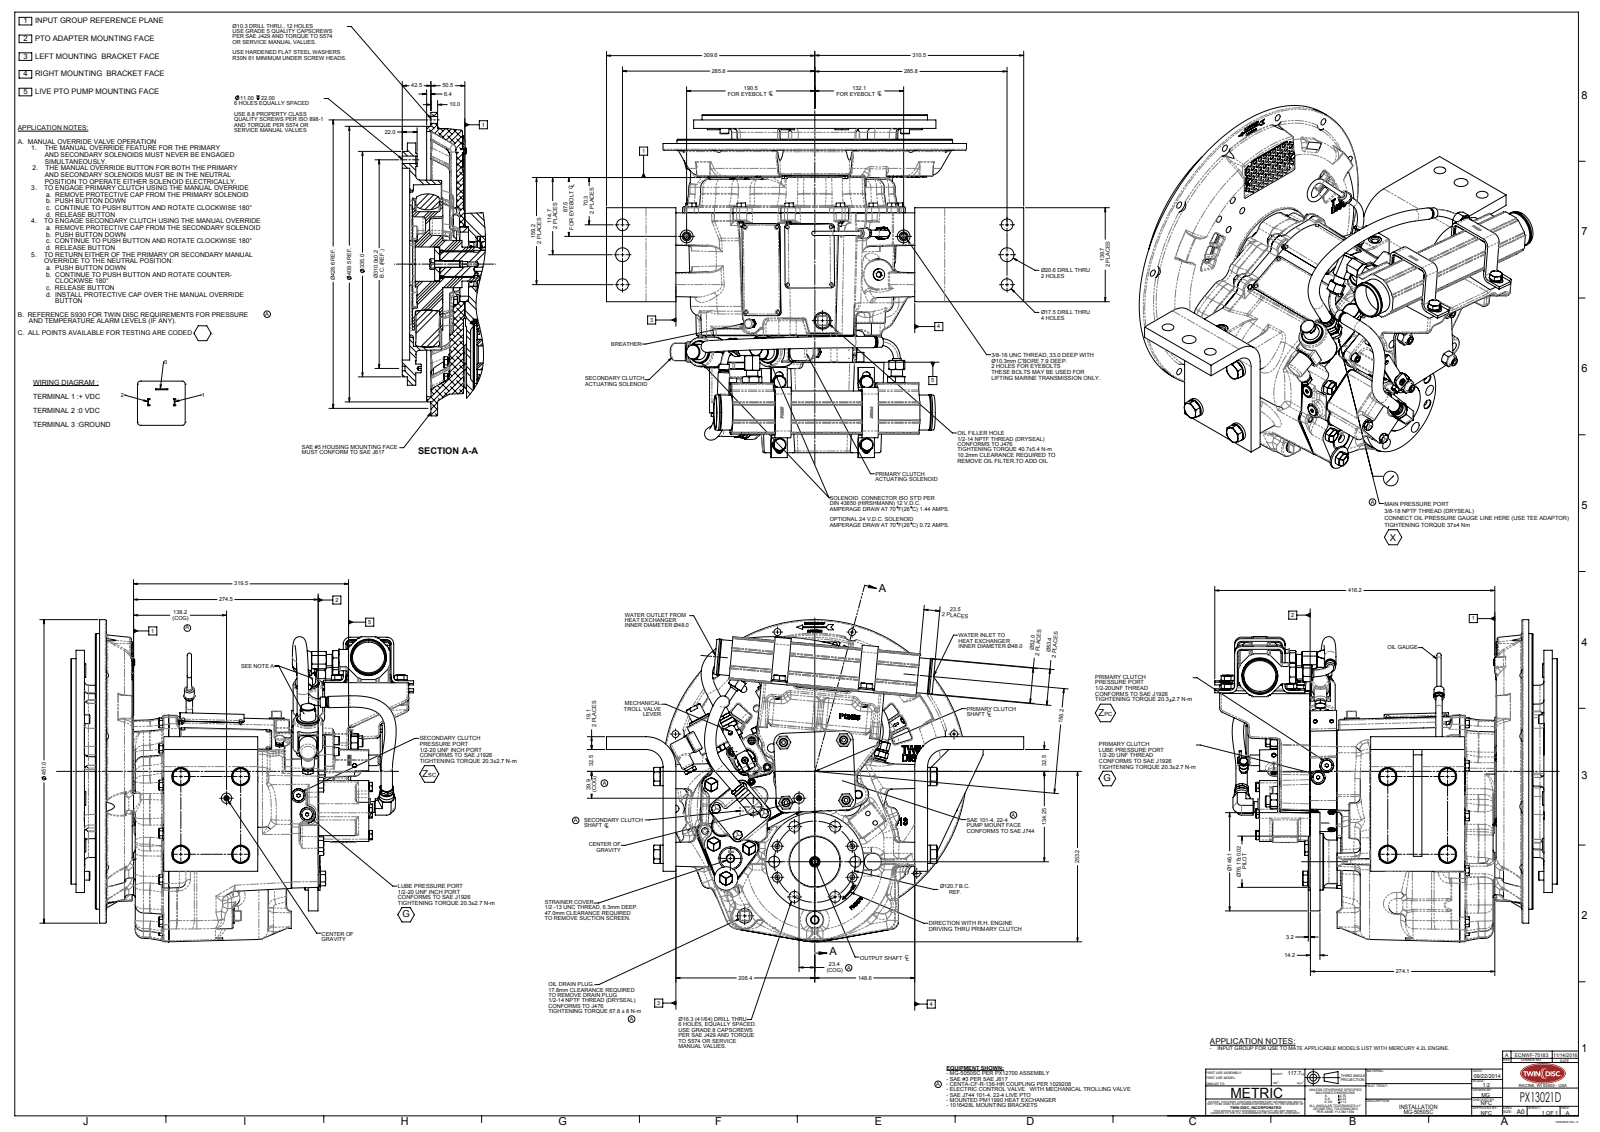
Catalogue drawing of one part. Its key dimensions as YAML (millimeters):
part_name: "PX13021D"
step_written_by: "SolidWorks 2010 (AUTOMOTIVE_DESIGN)"
units: millimeters
bodies: {solids: 0, faces: 4591, planar: 1174, cylindrical: 1264, other: 2153}
overall_size: [620.1, 509.18, 478.74]
round_holes:
  - {diameter: 7, count: 51}
  - {diameter: 10.32, count: 15}
  - {diameter: 11, count: 6}
  - {diameter: 16.27, count: 6}
  - {diameter: 20.64, count: 6}
  - {diameter: 7.14, count: 4}
  - {diameter: 10.3, count: 4}
  - {diameter: 12.7, count: 4}
  - {diameter: 14.29, count: 4}
  - {diameter: 17.46, count: 4}
  - {diameter: 6.8, count: 3}
  - {diameter: 7.94, count: 3}
round_bosses_or_shafts:
  - {diameter: 27.23, count: 4}
  - {diameter: 23.62, count: 4}
  - {diameter: 19, count: 4}
  - {diameter: 16.9, count: 4}
  - {diameter: 15.87, count: 4}
  - {diameter: 12.54, count: 4}
  - {diameter: 19.85, count: 3}
  - {diameter: 6.35, count: 3}
partial_cylinders:
  - {radius: 1.5, count: 87}
  - {radius: 8.13, count: 55}
  - {radius: 1.52, count: 50}
  - {radius: 2.5, count: 47}
  - {radius: 0.4, count: 32}
  - {radius: 6.5, count: 29}
  - {radius: 8, count: 28}
  - {radius: 13, count: 24}
face_to_face_distances: [19.05, 236.3, 307.26, 70.96, 374.04, 0.79, 237.09, 308.05, 4.54, 232.55]
hole_center_spacings: [214.3, 214.31, 371.19, 10, 110.93, 303.07, 414.01, 20]
